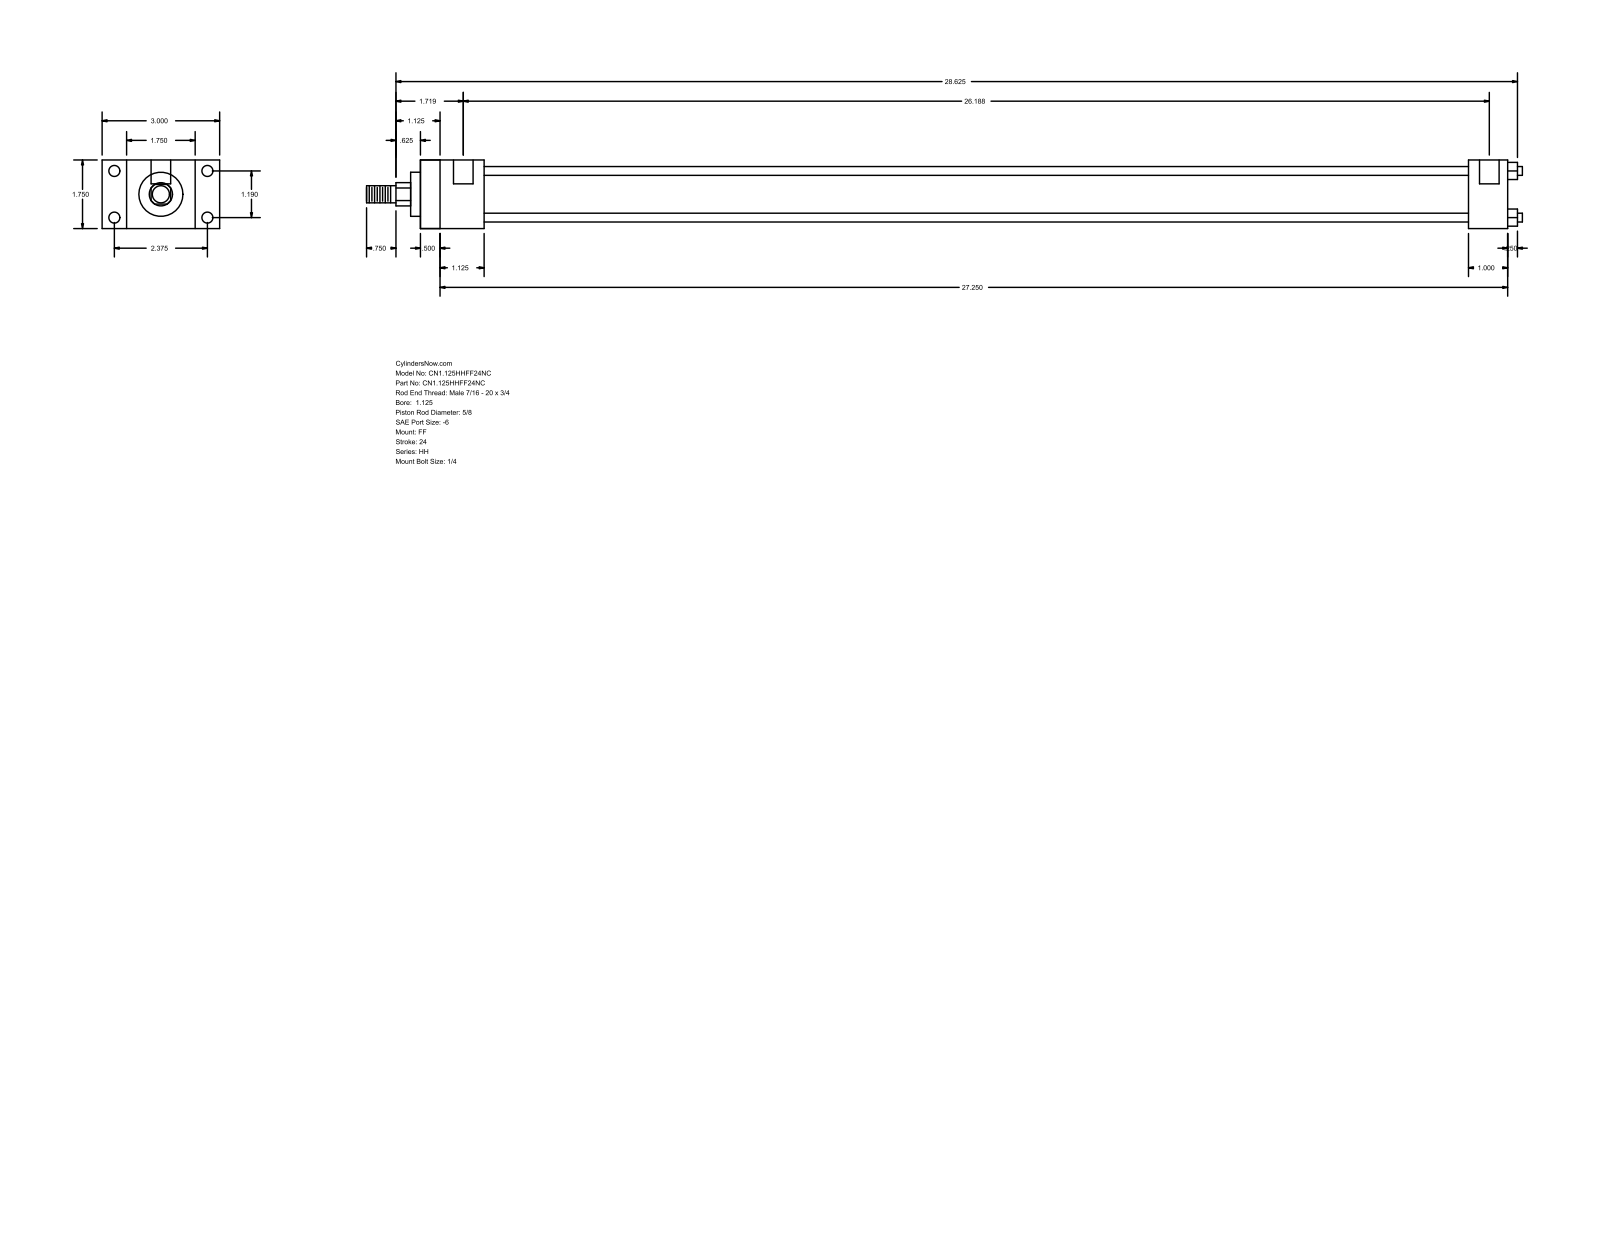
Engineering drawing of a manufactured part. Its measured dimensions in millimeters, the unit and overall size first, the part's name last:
Units: millimetres
Overall size (bounding box): 749.3 × 76.2 × 44.45
Round holes (diameter × count): ⌀5.56 ×4, ⌀7.14 ×4, ⌀12.7 ×2
Round bosses / shafts (diameter × count): ⌀5.71 ×4, ⌀34.92 ×1, ⌀28.57 ×1, ⌀15.88 ×1, ⌀11.11 ×1
Partial cylindrical surfaces — rounded edges, fillets, slot ends (radius × count): R7.54 ×1
Main face-to-face distances: 44.46, 704.85, 15.87, 12.69, 692.16, 28.58, 60.33, 25.4, 41.27, 679.45
Hole centre spacings: 30.22, 60.32, 67.47, 661.99, 3.17, 665.16
Bodies: 0 solids, 92 faces (64 planar, 28 cylindrical, 0 other)
Part name (STEP PRODUCT): HH_FF__0112_0.625
STEP written by: GSSL Pune (CONFIG_CONTROL_DESIGN)
